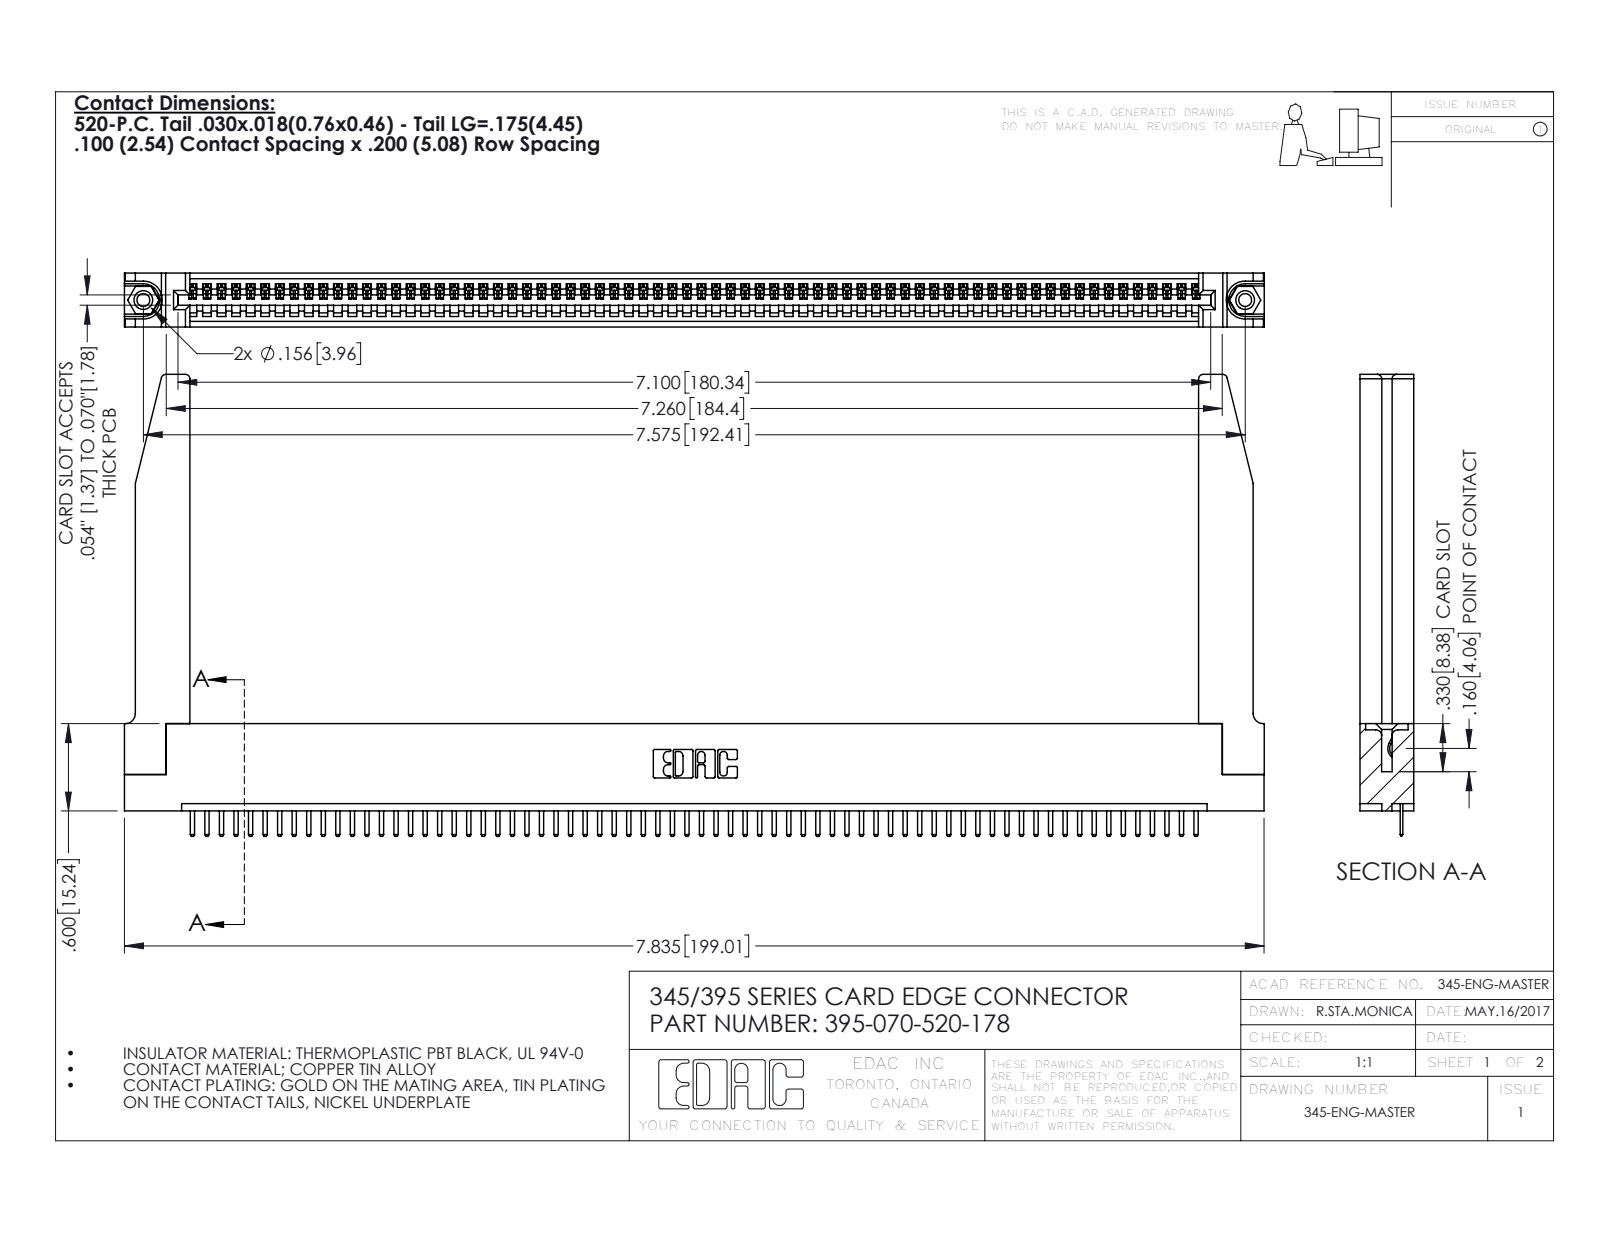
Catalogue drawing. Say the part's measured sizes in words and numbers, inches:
The part is named "345-250-001_345-250-001-102; 345 Part_Flush Mounting Lugs - 0.156 Dia-TH; 345-220-078_345-220-078; 395-070-520-178 (+1 more)". Its 3-D file was written by "SolidWorks 2016 (CONFIG_CONTROL_DESIGN)". It is 75 solids with 4700 faces: 3162 planar, 1486 cylindrical and 52 other. Overall it measures 7.836 by 3.175 by 0.37 inches. Its volume is 1.63 cubic inches and its surface area 49.18 square inches. Round holes: 2 of diameter 0.089, 2 of diameter 0.125, 2 of diameter 0.156, 1 of diameter 0.064. Round bosses or shafts: 2 of diameter 0.155. Partial cylindrical surfaces (rounded edges, fillets, slot ends): 142 of radius 0.01, 140 of radius 0.006, 22 of radius 0.01, 8 of radius 0.03, 6 of radius 0.007, 6 of radius 0.031, 3 of radius 0.026, 2 of radius 0.031. The main face-to-face distances are 0.37, 0.072, 0.298, 0.2, 0.098, 0.272, 0.025, 0.225, 0.072, 0.149. The hole center spacings are 0.27, 7.339, 7.575.
